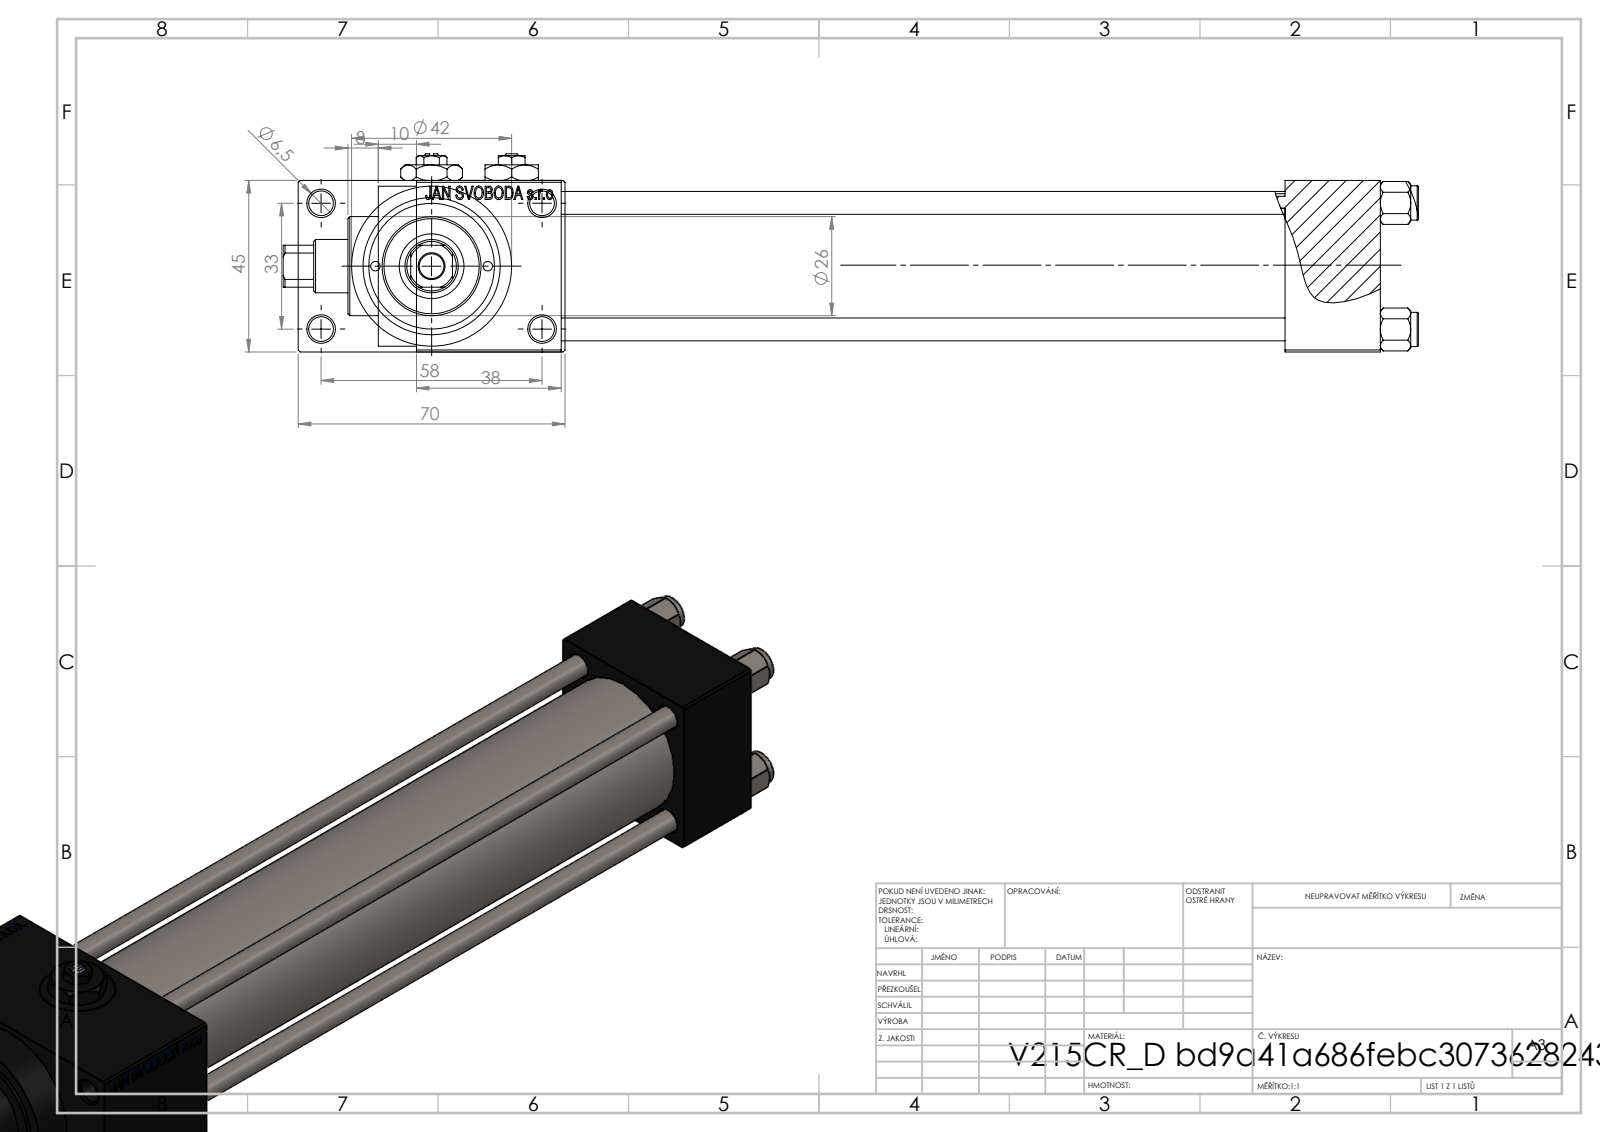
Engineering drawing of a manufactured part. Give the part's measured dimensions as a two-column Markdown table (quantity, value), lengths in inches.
| quantity | value |
| --- | --- |
| part name | V215CR_D_TYCINKA; V215CR_D_Body; V215CR_VCP_D; V215_VC_A (+2 more) |
| STEP written by | SolidWorks 2019 (CONFIG_CONTROL_DESIGN) |
| units | inches |
| bodies | 12 solids, 1157 faces (521 planar, 96 cylindrical, 540 other) |
| overall size | 11.732 × 2.756 × 2.047 |
| volume | 19.14 in³ |
| surface area | 191.4 in² |
| round holes (diameter × count) | 0.256 × 5, 0.236 × 4, 0.518 × 3, 0.787 × 3, 0.098 × 2, 0.276 × 2, 0.551 × 1, 0.669 × 1, 0.945 × 1, 1.26 × 1, 1.299 × 1 |
| round bosses / shafts (diameter × count) | 0.354 × 4, 1.654 × 1, 1.496 × 1, 1.024 × 1 |
| partial cylindrical surfaces (radius × count) | 0.256 × 1 |
| main face-to-face distances | 1.772, 0.984, 0.492, 7.48, 8.465, 2.264, 8.976, 1.496, 9.961, 2.756 |
| hole center spacings | 0.488, 0.657, 0.858, 0.924, 1.307, 1.314, 1.392, 1.396 |
